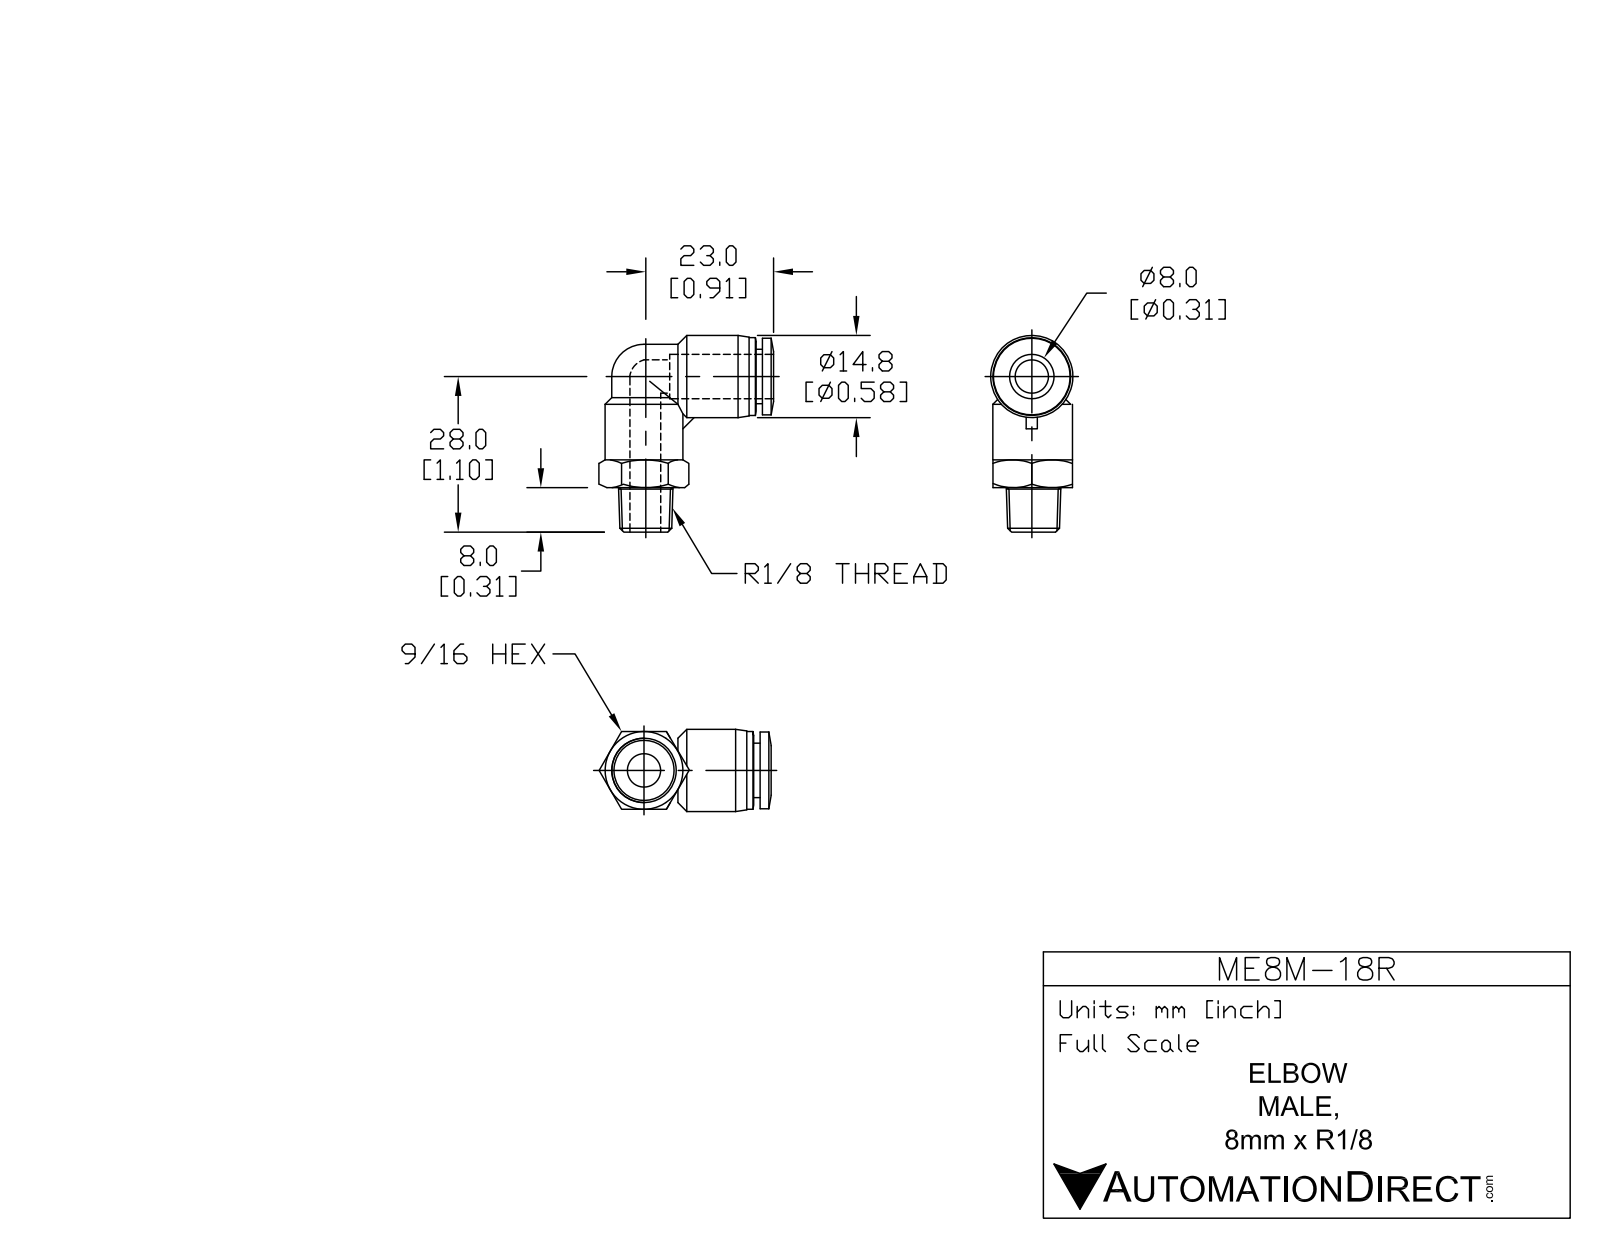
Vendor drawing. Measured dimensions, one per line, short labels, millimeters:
name: ME8M-18R
written by: SolidWorks 2015 (AUTOMOTIVE_DESIGN)
unit: mm
bodies: 1 solid, 68 faces (16 planar, 19 cylindrical, 33 other)
size: 35.4 × 31 × 14.8
volume: 4 800 mm³; area: 3 534 mm²
holes: 2× ⌀6, 1× ⌀8.3
bosses: 2× ⌀14, 1× ⌀14.8, 1× ⌀13.8, 1× ⌀11.6, 1× ⌀9.8
rounds: 1× R5.8
face distances: 14, 1.1, 8, 15.1, 16.3, 2, 18.3, 3.1, 6, 13.9
